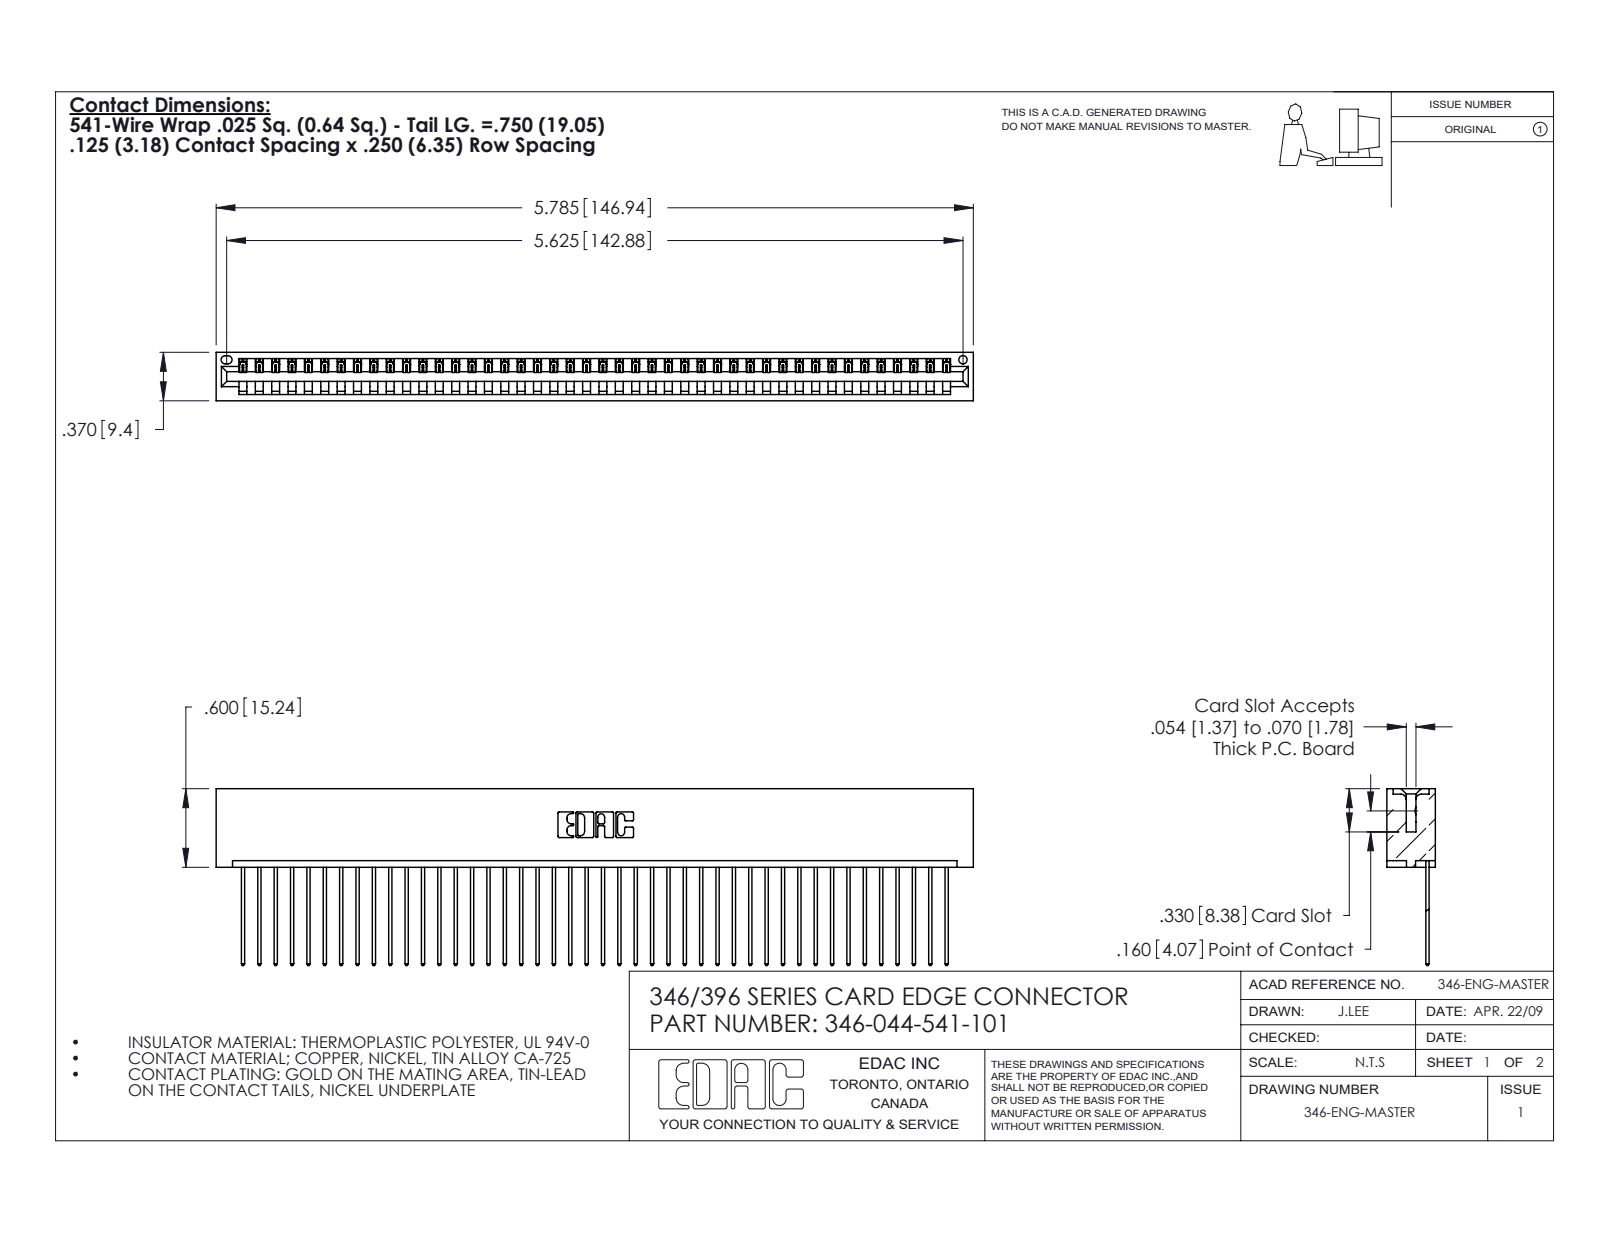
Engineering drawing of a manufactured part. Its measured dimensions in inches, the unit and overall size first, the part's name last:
Units: inches
Overall size (bounding box): 5.785 × 1.35 × 0.37
Round holes (diameter × count): ⌀0.064 ×1
Partial cylindrical surfaces — rounded edges, fillets, slot ends (radius × count): R0.006 ×88, R0.01 ×88, R0.01 ×22, R0.007 ×6, R0.031 ×6, R0.026 ×3, R0.031 ×2, R0.04 ×2
Main face-to-face distances: 0.048, 0.322, 0.37, 0.25, 0.072, 0.298, 0.025, 0.148, 0.222, 0.1
Volume: 0.902 in³ · Surface area: 30.12 in²
Bodies: 45 solids, 2666 faces (1832 planar, 834 cylindrical, 0 other)
Part name (STEP PRODUCT): 346 Part_No Mounting Lugs; 346-044-541-101; 345-292-001_345-293-141
STEP written by: SolidWorks 2020 (CONFIG_CONTROL_DESIGN)
